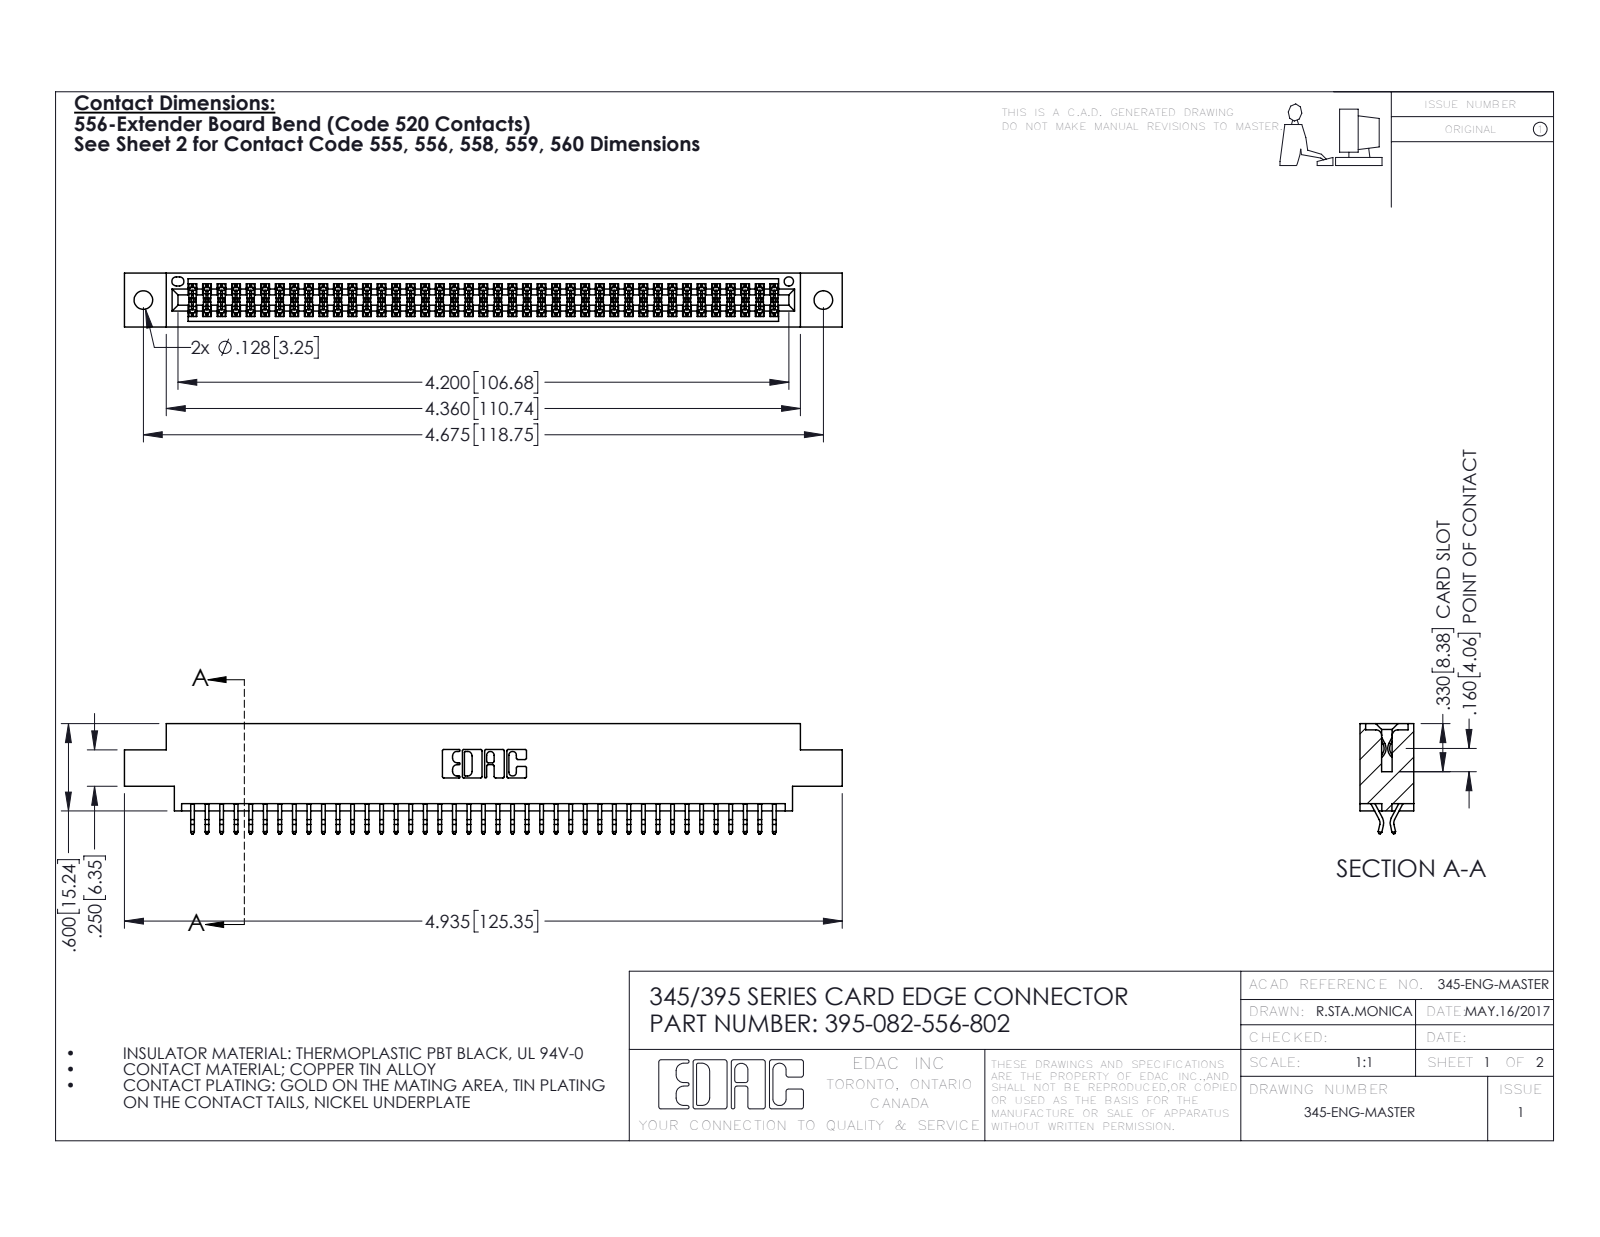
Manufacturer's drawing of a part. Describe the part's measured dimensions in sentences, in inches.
The part is named "345-292-001_556 Tail; 395-082-556-802; 345 Part_0.170 Offset - 0.128 Dia". Its 3-D file was written by "SolidWorks 2016 (CONFIG_CONTROL_DESIGN)". It is 83 solids with 4722 faces: 3118 planar, 1604 cylindrical and 0 other. Overall it measures 4.935 by 0.757 by 0.37 inches. Its volume is 0.733 cubic inches and its surface area 27.18 square inches. Round holes: 2 of diameter 0.128, 1 of diameter 0.064. Partial cylindrical surfaces (rounded edges, fillets, slot ends): 123 of radius 0.006, 22 of radius 0.01, 6 of radius 0.007, 6 of radius 0.031, 3 of radius 0.026, 2 of radius 0.01, 2 of radius 0.014, 2 of radius 0.019. The main face-to-face distances are 0.298, 0.072, 0.37, 0.2, 0.025, 0.098, 0.272, 0.225, 0.175, 0.149. The hole center spacings are 0.27, 4.439, 4.675.
